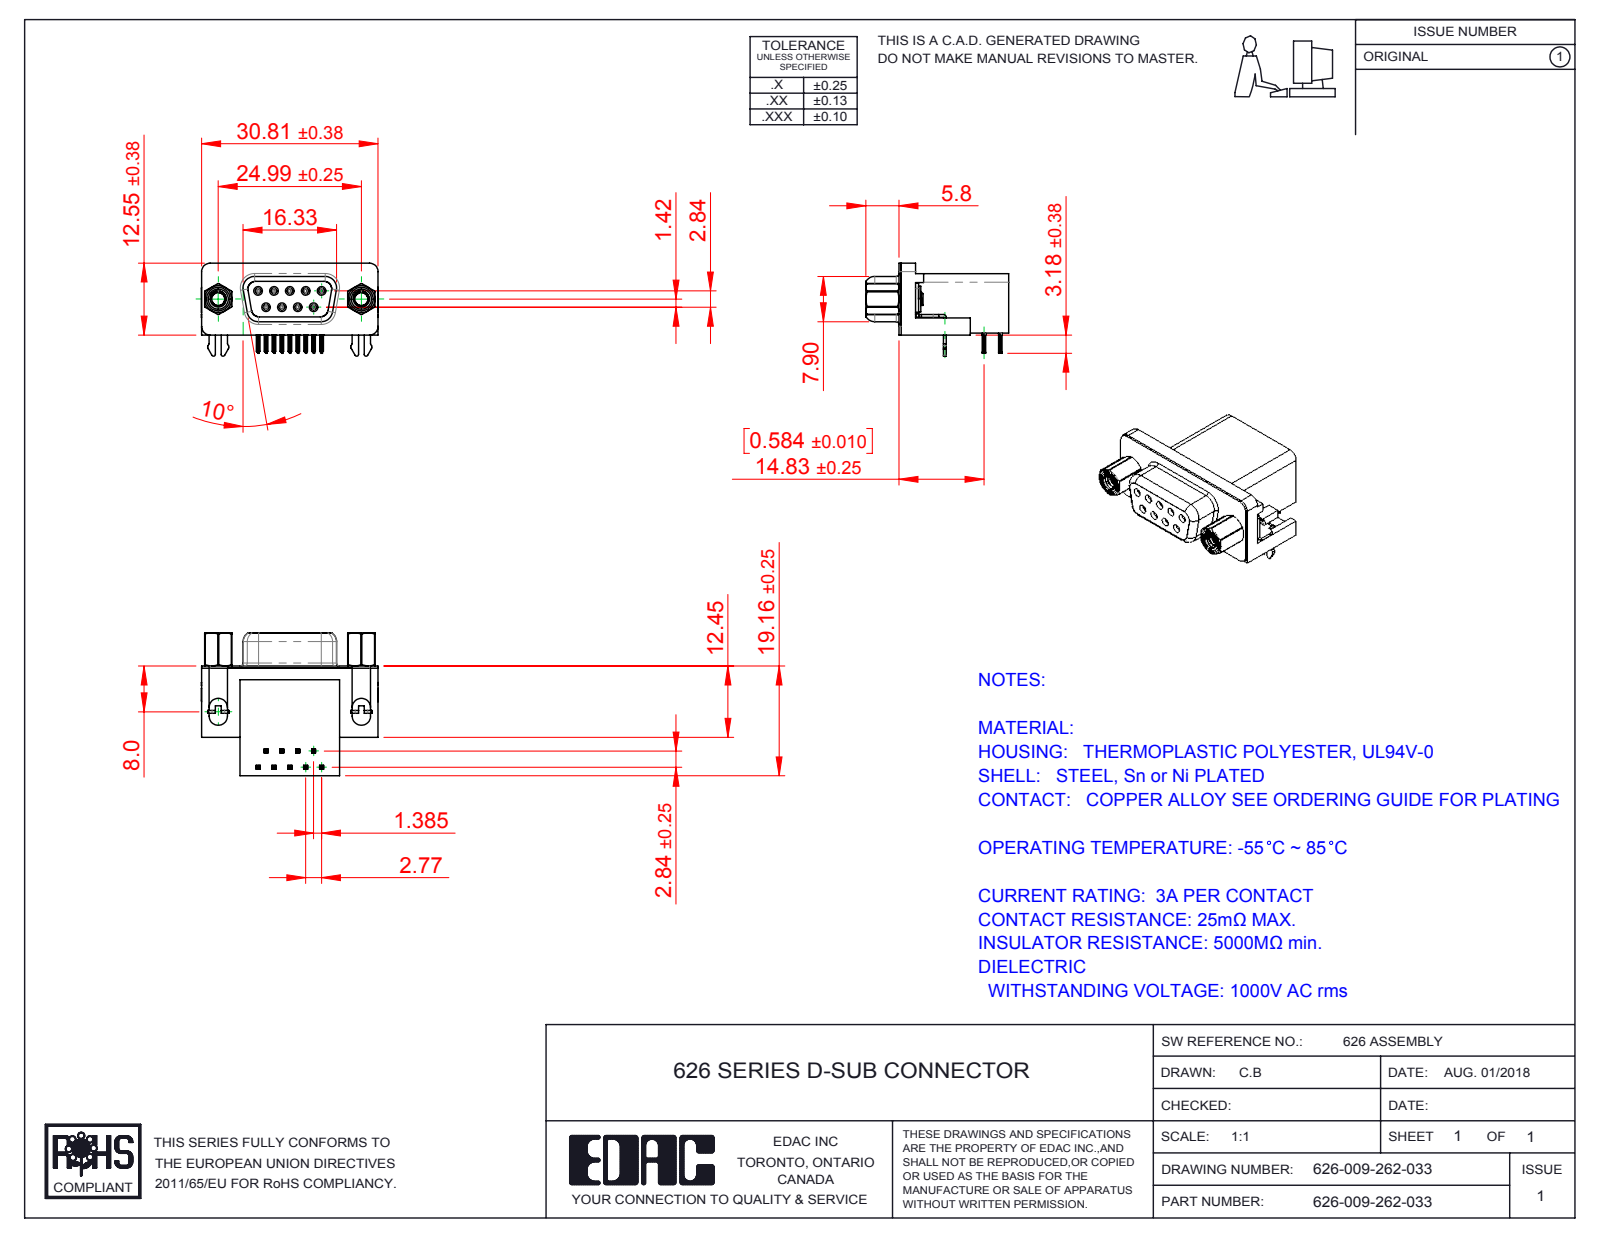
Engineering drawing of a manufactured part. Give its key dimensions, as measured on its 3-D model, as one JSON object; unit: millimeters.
{"part_name": "626 4-40 Hex Standoff 5; 626 Round Threaded Standoff; 626 2 Prong Board Lock; 626 Contact Top (+4 more)", "step_written_by": "SolidWorks 2016 (CONFIG_CONTROL_DESIGN)", "units": "millimeters", "bodies": {"solids": 17, "faces": 1732, "planar": 730, "cylindrical": 504, "other": 498}, "overall_size": [30.89, 24.96, 16.25], "volume_mm3": 5270, "surface_area_mm2": 6479, "round_holes": [[0.8, 9], [0.9, 9], [2.29, 2], [2.3, 2], [3.1, 2], [4, 2], [4.8, 2], [5, 2]], "round_bosses_or_shafts": [[1.2, 9], [4.9, 2], [4.7, 2], [4.5, 2], [3.85, 2], [2.79, 2]], "partial_cylinders_radius": [[0.1, 72], [0.15, 36], [0.35, 18], [1, 18], [0.5, 10], [0.34, 9], [1.35, 8], [1.6, 8]], "face_to_face_distances": [0.4, 10.34, 0.35, 18.76, 19.16, 16.26, 6.2, 2.9, 2.5, 10.69], "hole_center_spacings": [3.16, 2.77, 5.54, 5.03, 5.04, 8.31, 7.48, 7.49]}
